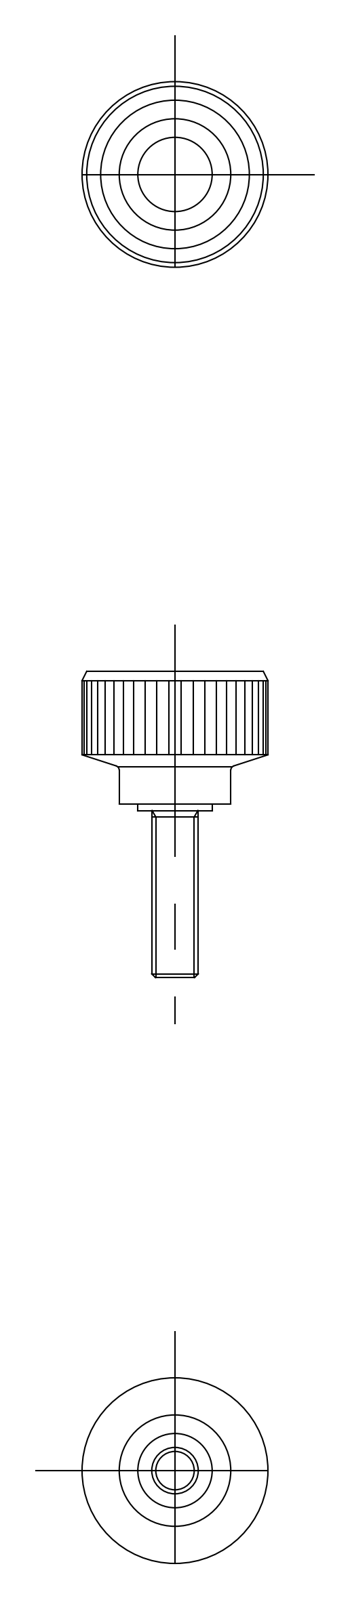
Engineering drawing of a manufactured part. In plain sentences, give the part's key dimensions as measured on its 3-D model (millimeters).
The part is named "screw; knob; KKM_20_M5_18_5028_36". Its 3-D file was written by "CADfix (AUTOMOTIVE_DESIGN)". It is 2 solids with 35 faces: 0 planar, 0 cylindrical and 35 other. Overall it measures 33 by 20 by 20 millimeters. Its volume is 3 099 cubic millimeters and its surface area 2 216 square millimeters.
